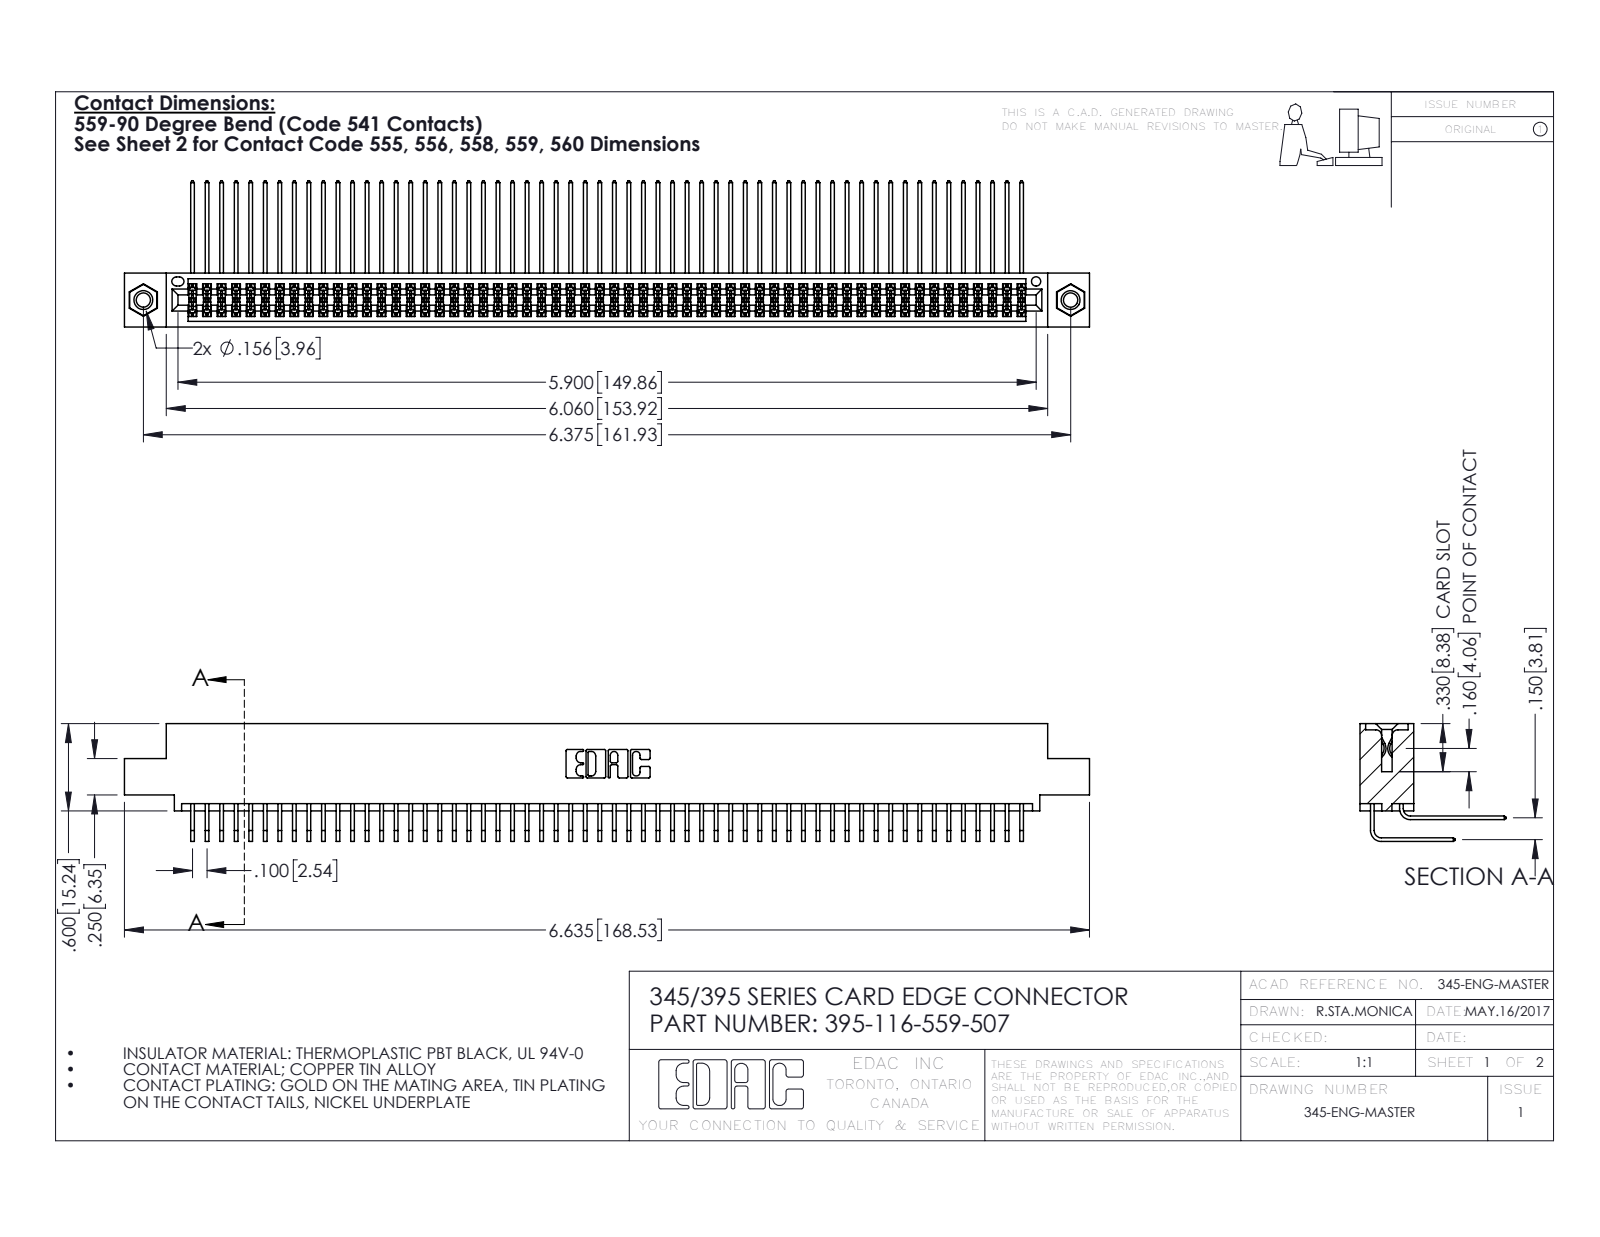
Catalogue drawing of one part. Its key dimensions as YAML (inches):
part_name: "345 Part_0.110 Offset - 0.156 Dia-TI; 345-292-001_558 559 Tail - 1; 395-116-559-507; 345-250-001_345-250-005-103 (+1 more)"
step_written_by: "SolidWorks 2016 (CONFIG_CONTROL_DESIGN)"
units: inches
bodies: {solids: 119, faces: 6222, planar: 4176, cylindrical: 2030, other: 16}
overall_size: [6.635, 1.005, 0.809]
volume: 1.044
surface_area: 44.73
round_holes:
  - {diameter: 0.098, count: 2}
  - {diameter: 0.125, count: 2}
  - {diameter: 0.156, count: 2}
  - {diameter: 0.064, count: 1}
round_bosses_or_shafts:
  - {diameter: 0.155, count: 2}
partial_cylinders:
  - {radius: 0.006, count: 174}
  - {radius: 0.01, count: 22}
  - {radius: 0.007, count: 6}
  - {radius: 0.031, count: 6}
  - {radius: 0.026, count: 3}
  - {radius: 0.014, count: 2}
  - {radius: 0.019, count: 2}
  - {radius: 0.022, count: 2}
face_to_face_distances: [0.072, 0.298, 0.2, 0.37, 0.098, 0.272, 0.025, 0.225, 0.175, 0.15]
hole_center_spacings: [0.27, 6.139, 6.375]
